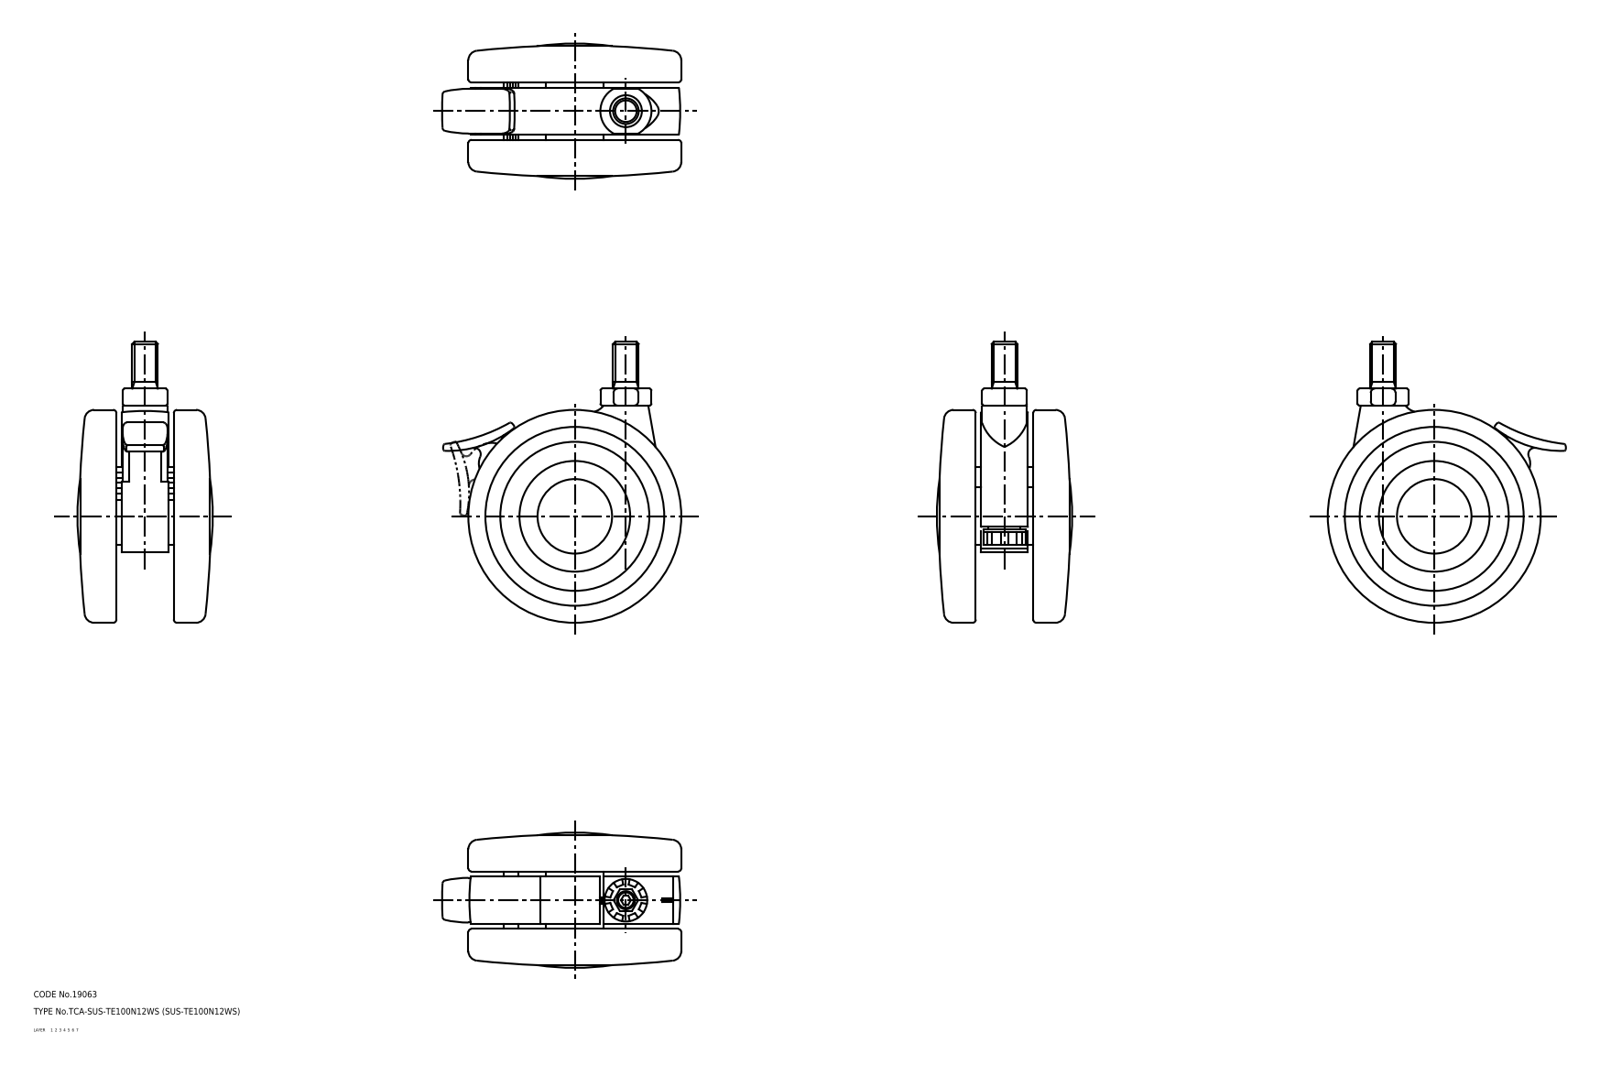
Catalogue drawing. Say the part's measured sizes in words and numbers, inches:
The part is named "wheel_mr; lever; wheel; main shaft (+1 more)". Its 3-D file was written by "CADfix (AUTOMOTIVE_DESIGN)". It is 5 solids with 225 faces: 0 planar, 0 cylindrical and 225 other. Overall it measures 5.197 by 4.404 by 2.503 inches. Its volume is 19.24 cubic inches and its surface area 119.9 square inches.
